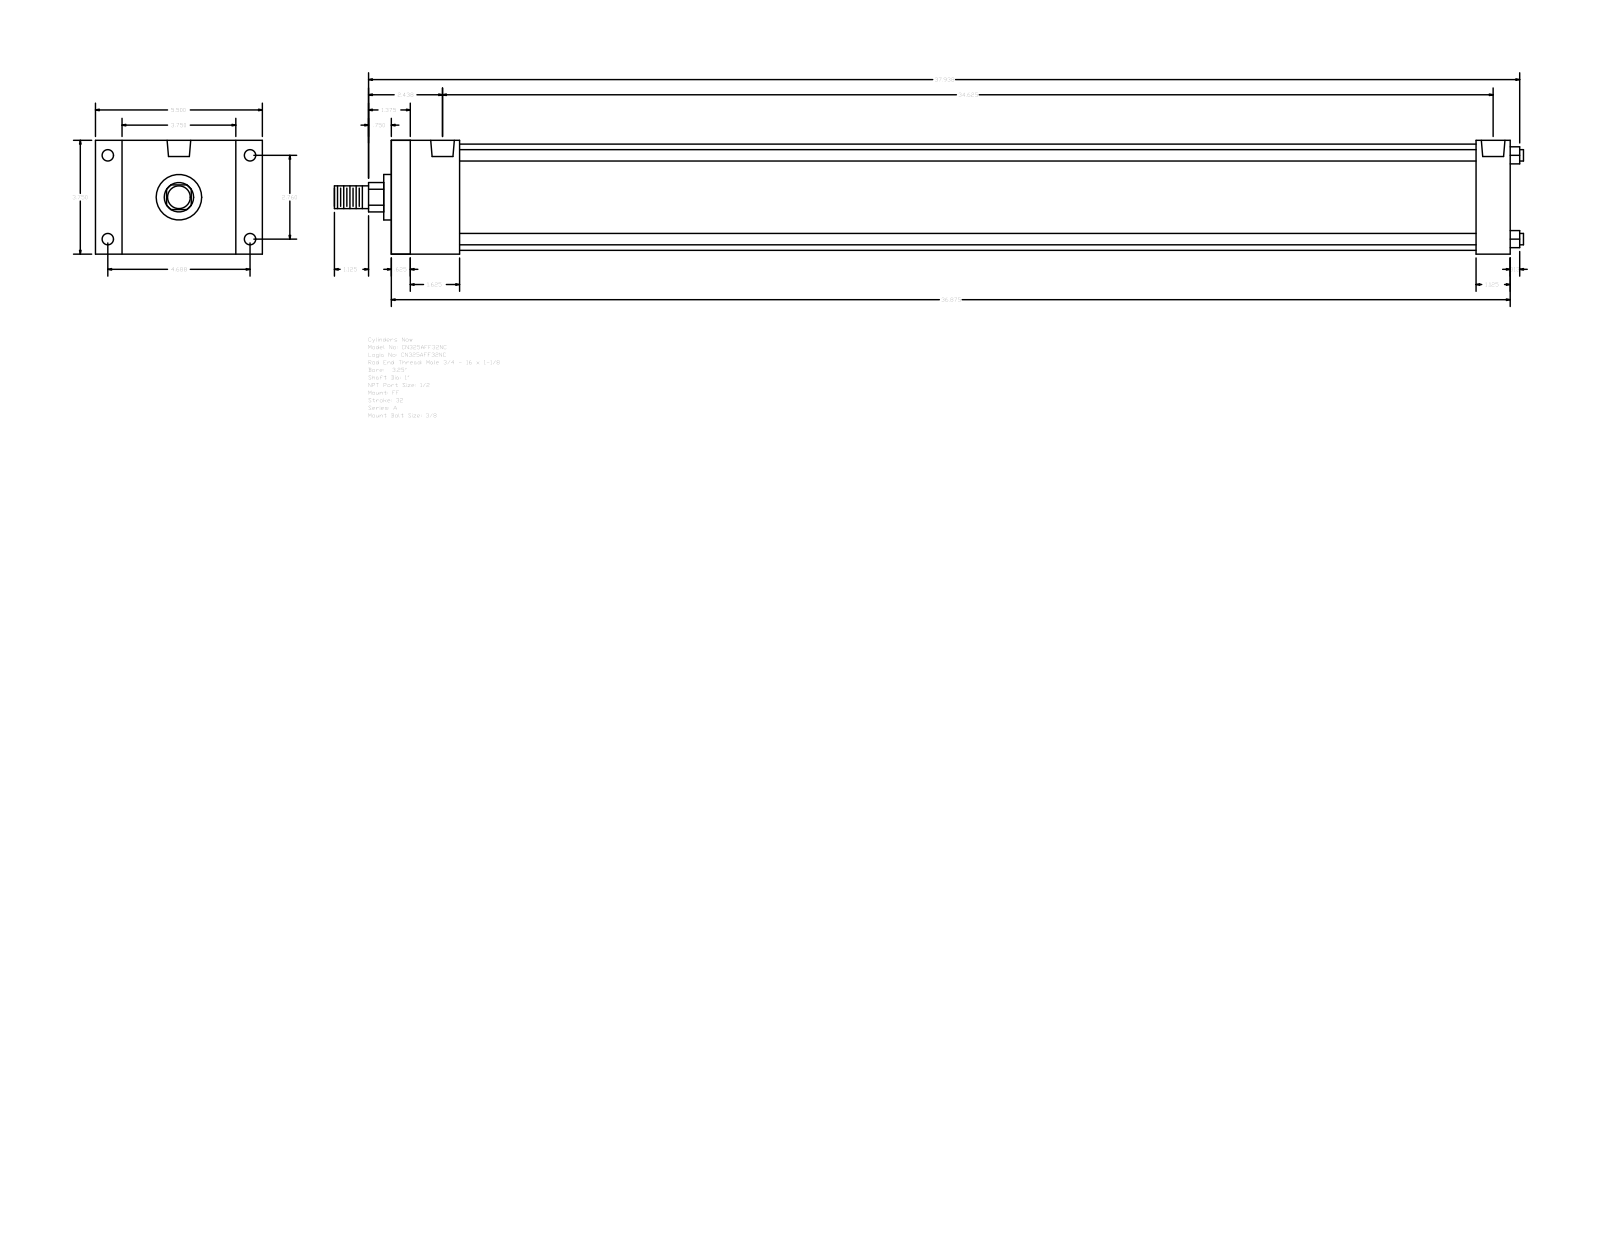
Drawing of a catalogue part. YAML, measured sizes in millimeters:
part_name: "A_FF__0325_1"
step_written_by: "GSSL Pune (CONFIG_CONTROL_DESIGN)"
units: millimeters
bodies: {solids: 0, faces: 92, planar: 64, cylindrical: 28, other: 0}
overall_size: [995.36, 139.7, 95.25]
round_holes:
  - {diameter: 8.73, count: 4}
  - {diameter: 9.53, count: 4}
  - {diameter: 19.77, count: 2}
round_bosses_or_shafts:
  - {diameter: 9.53, count: 4}
  - {diameter: 88.9, count: 1}
  - {diameter: 38.1, count: 1}
  - {diameter: 25.4, count: 1}
  - {diameter: 19.05, count: 1}
partial_cylinders:
  - {radius: 12.29, count: 1}
face_to_face_distances: [95.24, 936.62, 15.87, 920.75, 22.23, 117.47, 28.57, 57.15, 908.05, 41.28]
hole_center_spacings: [3.18, 70.1, 119.06, 138.16, 873.12, 876.3, 879.48]
